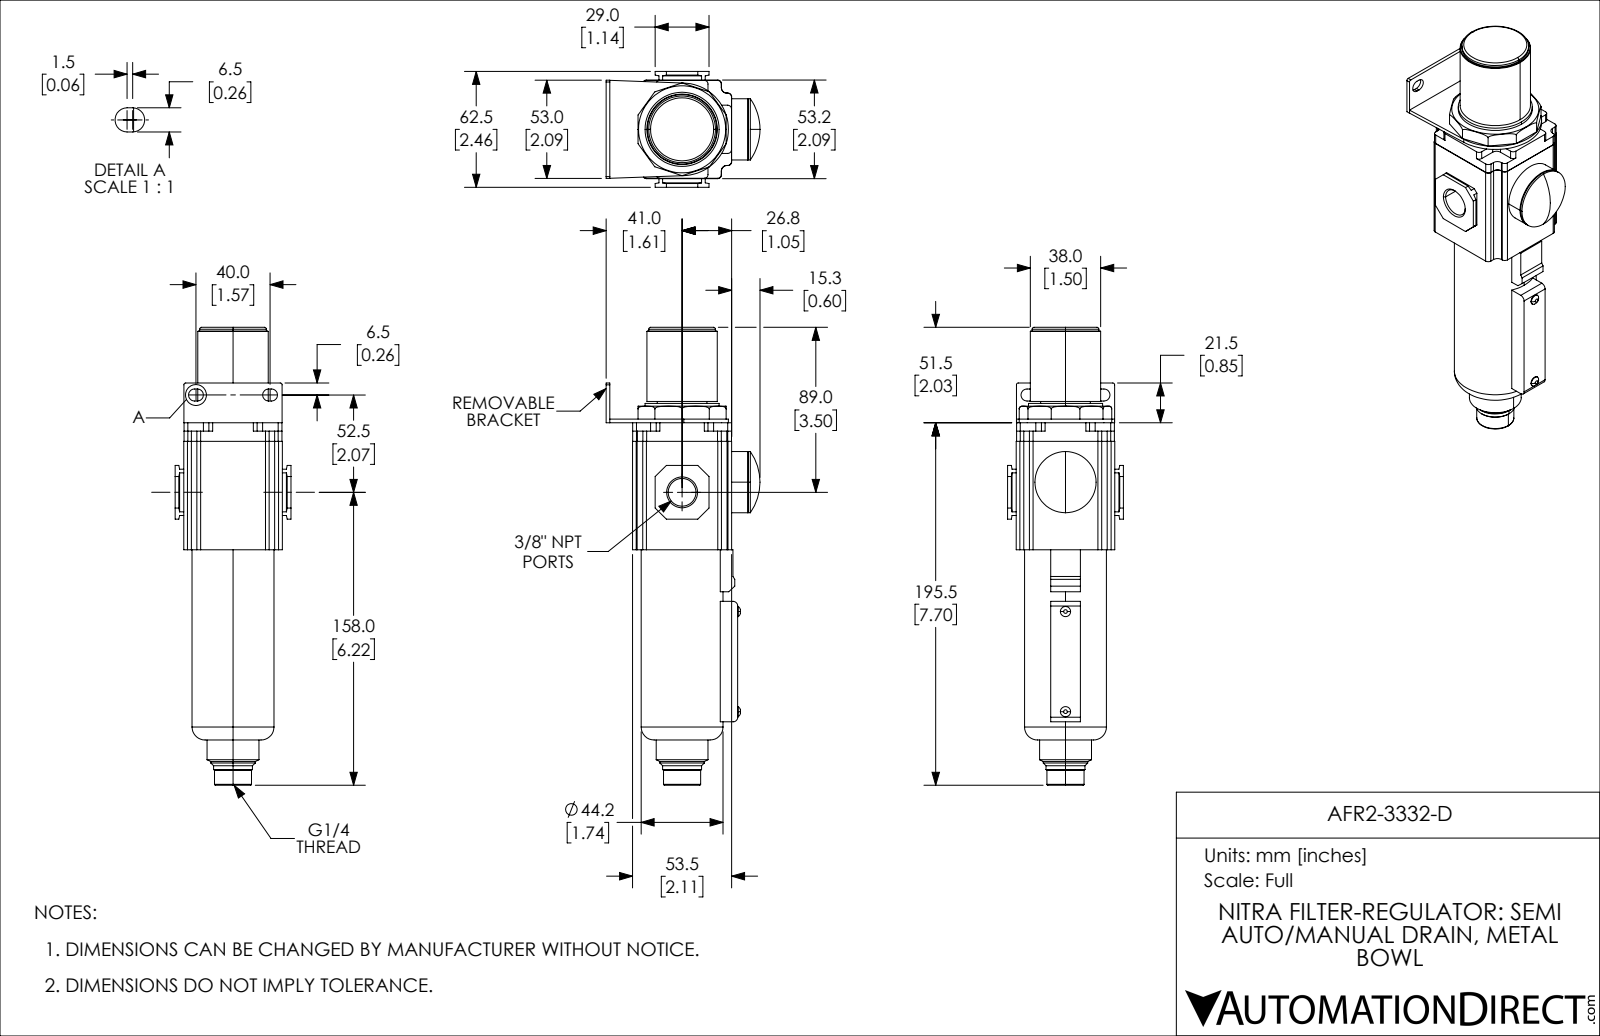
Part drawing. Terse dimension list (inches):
name: AFR2-3332-D
written by: SolidWorks 2019 (CONFIG_CONTROL_DESIGN)
unit: in
bodies: 1 solid, 235 faces (128 planar, 77 cylindrical, 30 other)
size: 9.724 × 3.269 × 2.461
volume: 26.78 in³; area: 81.99 in²
holes: 1× ⌀0.451, 1× ⌀0.589
bosses: 2× ⌀0.217, 1× ⌀1.74, 1× ⌀1.575, 1× ⌀1.496, 1× ⌀1.417, 1× ⌀1.299, 1× ⌀1.102, 1× ⌀1.054
rounds: 24× R0.079, 12× R0.118, 4× R0.128, 2× R0.039, 2× R0.098, 1× R0.984
face distances: 0.079, 2.094, 0.732, 1.362, 0.63, 2.106, 1.545, 0.561, 0.183, 0.915
